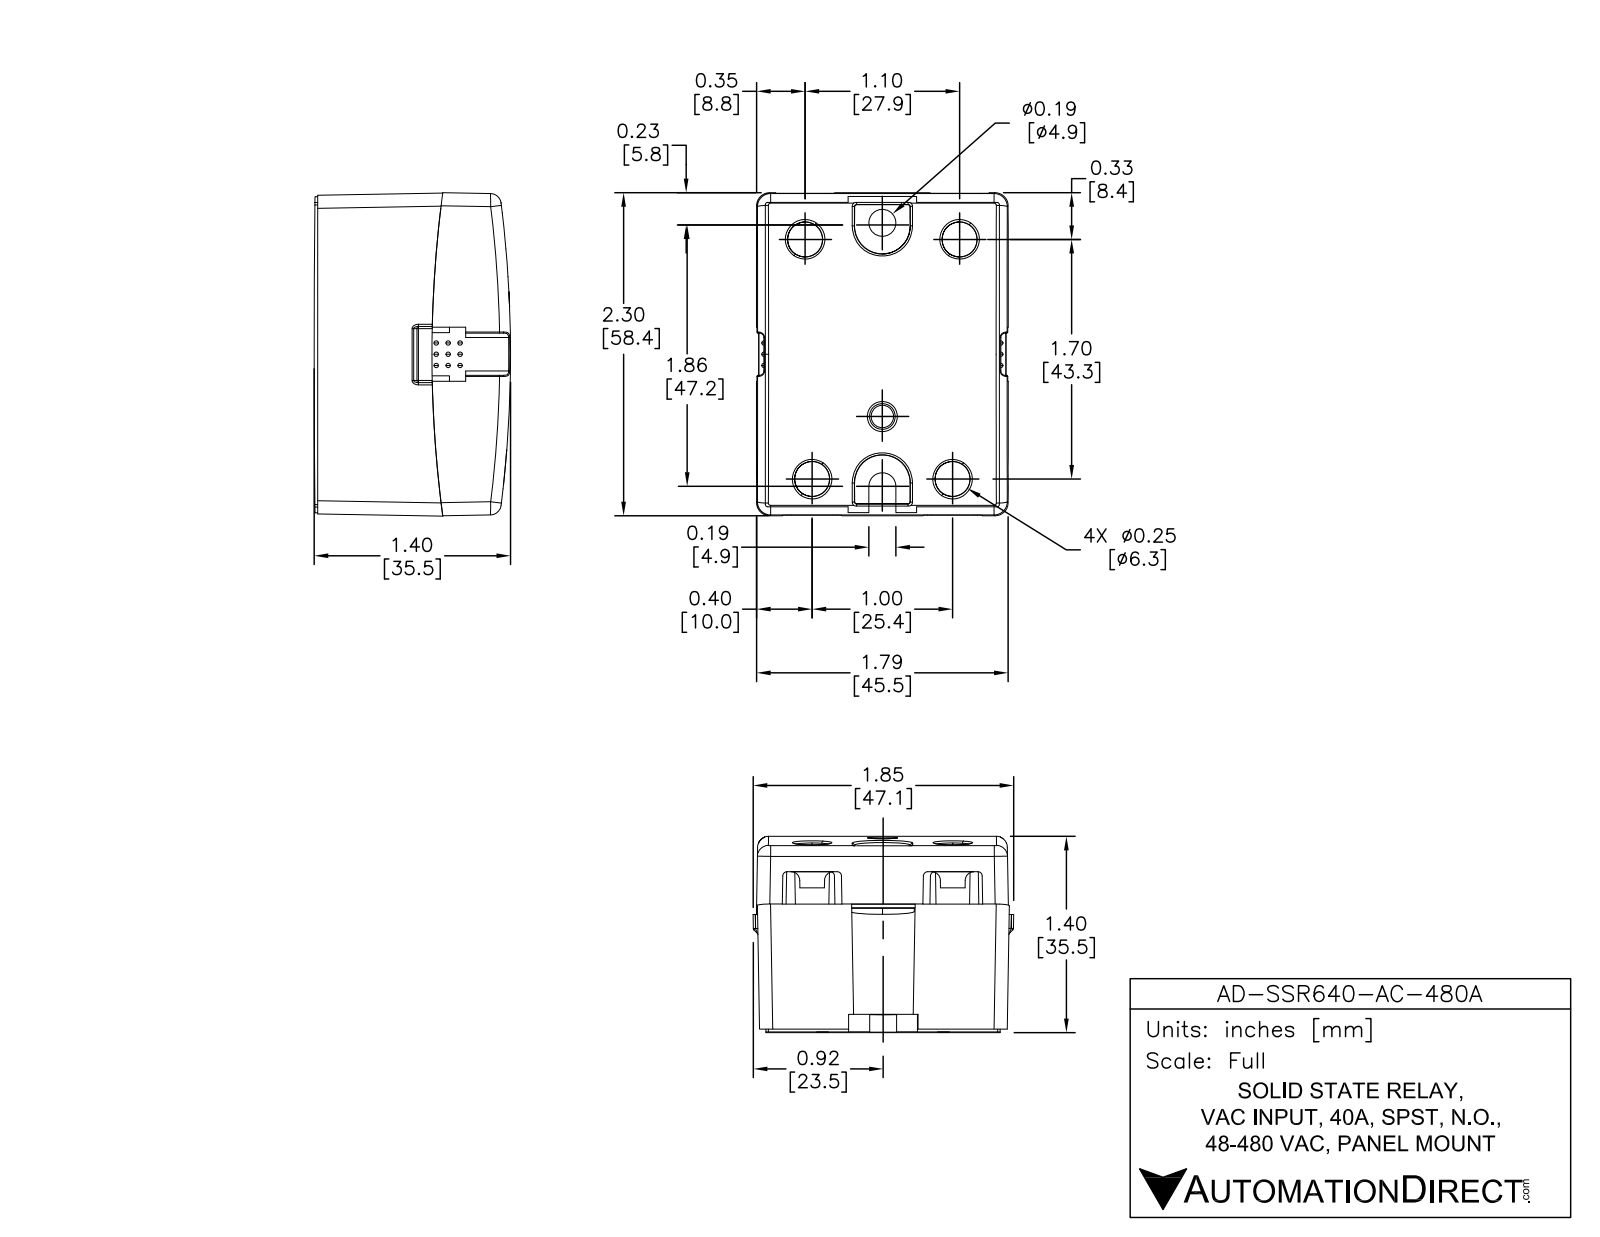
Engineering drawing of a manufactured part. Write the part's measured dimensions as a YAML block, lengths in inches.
part_name: "AD-SSR640-AC-480A"
step_written_by: "SolidWorks 2013 (AUTOMOTIVE_DESIGN)"
units: inches
bodies: {solids: 3, faces: 251, planar: 145, cylindrical: 95, other: 11}
overall_size: [2.3, 1.79, 1.4]
volume: 5.14
surface_area: 26.41
round_holes:
  - {diameter: 0.25, count: 4}
  - {diameter: 0.19, count: 1}
round_bosses_or_shafts:
  - {diameter: 0.4, count: 2}
  - {diameter: 0.35, count: 2}
  - {diameter: 0.3, count: 2}
  - {diameter: 0.25, count: 2}
  - {diameter: 0.2, count: 2}
  - {diameter: 0.2, count: 2}
partial_cylinders:
  - {radius: 0.03, count: 6}
  - {radius: 0.01, count: 4}
  - {radius: 0.04, count: 4}
  - {radius: 0.5, count: 4}
  - {radius: 0.194, count: 2}
  - {radius: 0.095, count: 1}
  - {radius: 0.5, count: 1}
  - {radius: 0.5, count: 1}
face_to_face_distances: [1.79, 2.3, 1.166, 0.25, 0.916, 0.671, 1.059, 0.5, 1.8, 0.08]
hole_center_spacings: [0.556, 0.565, 1, 1.1, 1.7, 1.701, 1.876, 1.879]
